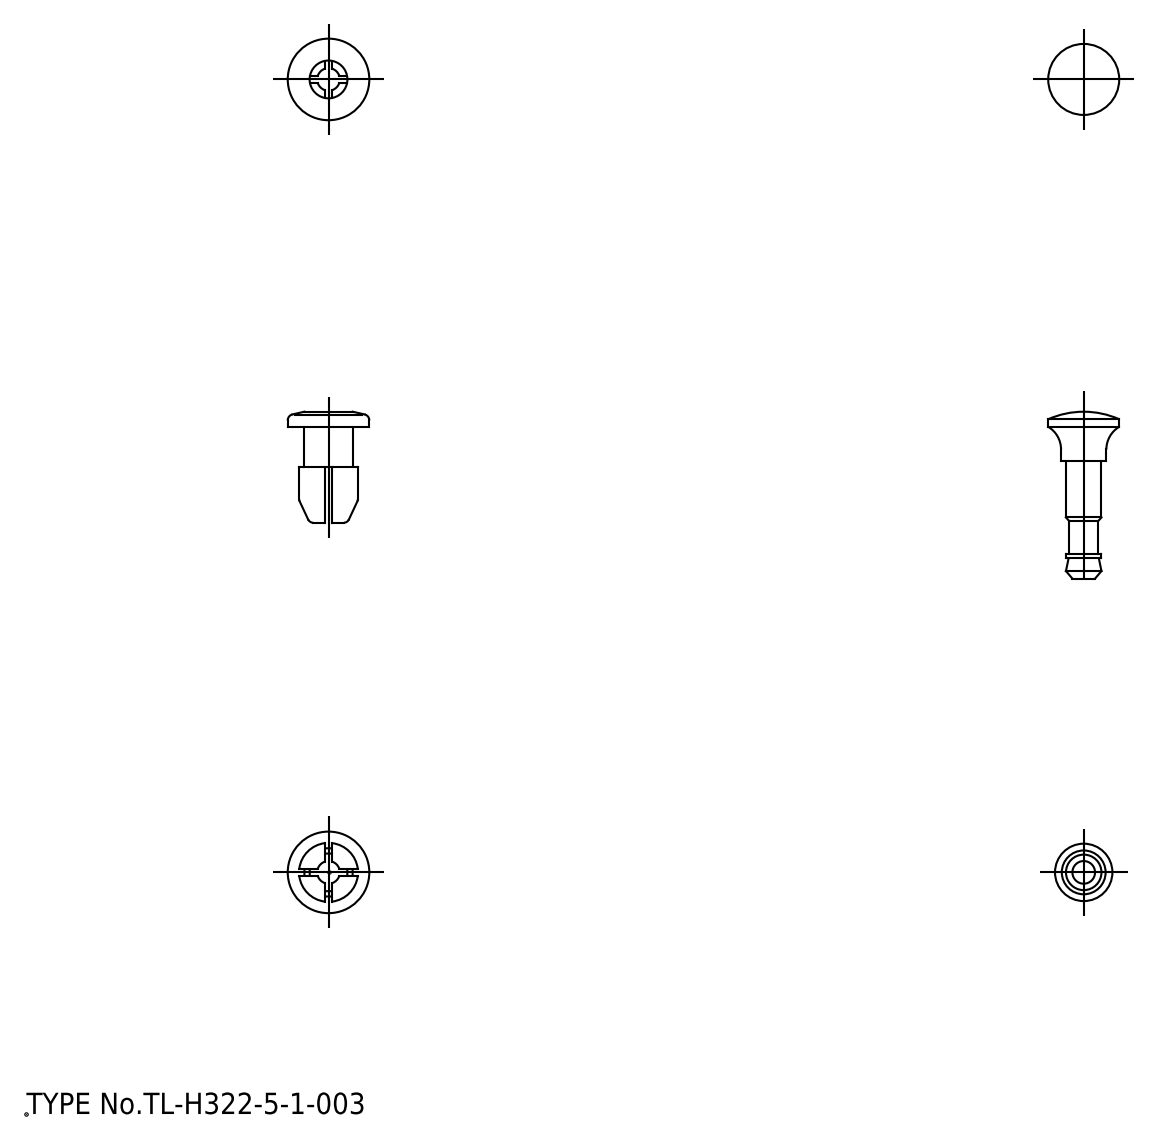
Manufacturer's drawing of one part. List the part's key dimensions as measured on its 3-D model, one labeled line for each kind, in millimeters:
Part name (STEP PRODUCT): grommet; plunger
STEP written by: spGate 18.9.1 (****-****-****-****) (AUTOMOTIVE_DESIGN)
Units: millimetres
Bodies: 2 solids, 80 faces (26 planar, 24 cylindrical, 30 other)
Overall size (bounding box): 24.1 × 10.8 × 10.8
Volume: 841 mm³ · Surface area: 1 186 mm²
Round holes (diameter × count): ⌀5 ×1
Round bosses / shafts (diameter × count): ⌀10.8 ×1, ⌀9.4 ×1, ⌀7.8 ×1, ⌀6.4 ×1, ⌀6 ×1, ⌀4.7 ×1, ⌀3.8 ×1
Partial cylindrical surfaces — rounded edges, fillets, slot ends (radius × count): R1.5 ×1
Main face-to-face distances: 1, 2, 5.3, 7.3, 10.2, 4.9, 2.9, 12.7, 2.7, 5.4
